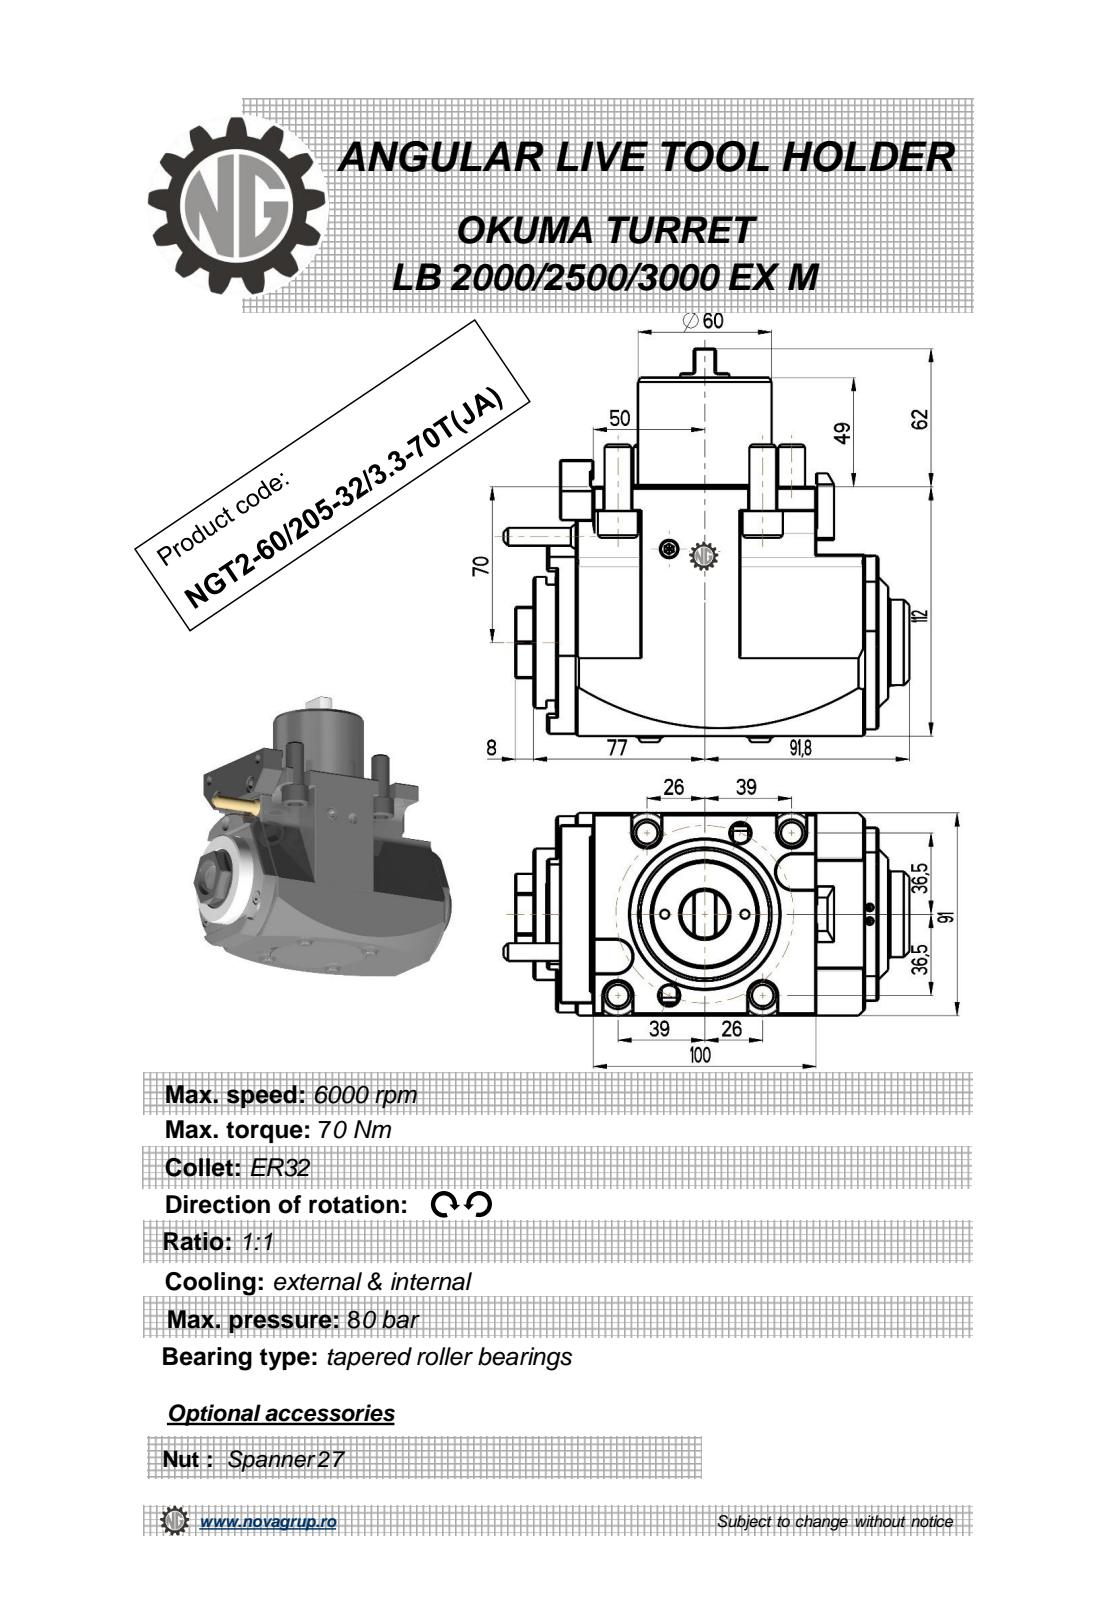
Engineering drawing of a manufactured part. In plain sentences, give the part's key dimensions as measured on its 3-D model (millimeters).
The part is named "NGT2_60_205_32_3_3_70T_JA". Its 3-D file was written by "PRO/ENGINEER BY PARAMETRIC TECHNOLOGY CORPORATION, 2010280 (CONFIG_CONTROL_DESIGN)". It is 1 solid with 759 faces: 402 planar, 191 cylindrical and 166 other. Overall it measures 182.14 by 176.75 by 91 millimeters. Its volume is 1 431 000 cubic millimeters and its surface area 112 535 square millimeters. Round holes: 3 of diameter 5, 2 of diameter 9, 1 of diameter 3, 1 of diameter 3.3, 1 of diameter 4.2, 1 of diameter 9.5, 1 of diameter 23, 1 of diameter 64. Round bosses or shafts: 4 of diameter 18, 4 of diameter 12, 4 of diameter 11.8, 4 of diameter 9.5, 2 of diameter 6, 2 of diameter 3, 1 of diameter 78, 1 of diameter 63.5. Partial cylindrical surfaces (rounded edges, fillets, slot ends): 24 of radius 0.36, 20 of radius 0.24, 12 of radius 0.15, 12 of radius 0.26, 10 of radius 0.31, 6 of radius 0.8, 4 of radius 6.5, 4 of radius 10. The main face-to-face distances are 91, 5.5, 49, 112, 101, 12, 106.5, 21, 11, 60. The hole center spacings are 39.85, 49.3, 82.46, 19.24, 32.21, 38.5, 50.45, 56.69.
